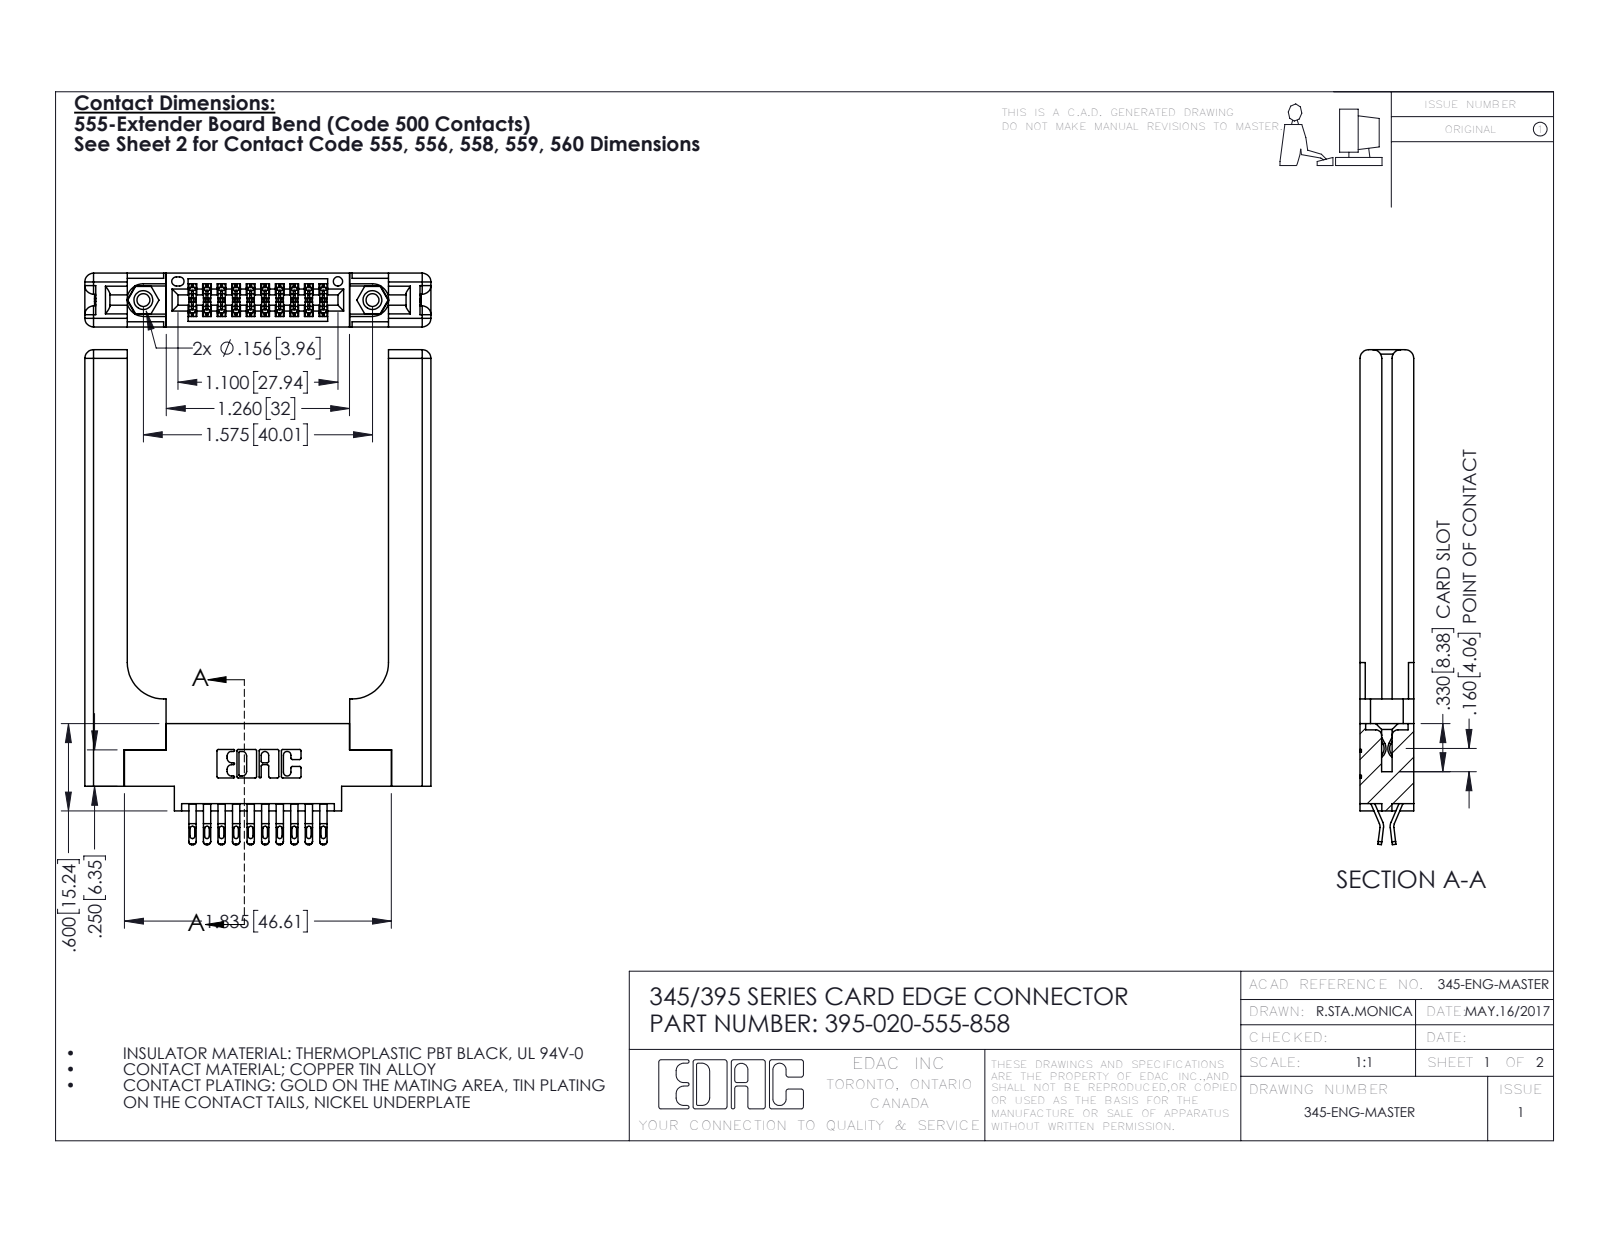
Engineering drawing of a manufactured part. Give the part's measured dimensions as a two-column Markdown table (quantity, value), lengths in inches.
| quantity | value |
| --- | --- |
| part name | 345 Part_0.170 Offset - 0.156 Dia-TH; 345-292-001_555 Tail; 345-250-001_345-250-001-102; 345-220-058_345-220-058 (+1 more) |
| STEP written by | SolidWorks 2016 (CONFIG_CONTROL_DESIGN) |
| units | inches |
| bodies | 25 solids, 1506 faces (852 planar, 594 cylindrical, 60 other) |
| overall size | 3.402 × 2.379 × 0.37 |
| volume | 0.854 in³ |
| surface area | 20.06 in² |
| round holes (diameter × count) | 0.089 × 2, 0.125 × 2, 0.156 × 2, 0.064 × 1 |
| round bosses / shafts (diameter × count) | 0.155 × 2 |
| partial cylindrical surfaces (radius × count) | 0.016 × 50, 0.02 × 40, 0.006 × 30, 0.01 × 22, 0.06 × 16, 0.007 × 6, 0.031 × 6, 0.026 × 3 |
| main face-to-face distances | 0.37, 0.072, 0.15, 0.22, 0.077, 0.148, 0.298, 1.796, 0.225, 0.12 |
| hole center spacings | 0.27, 1.344, 1.575 |
